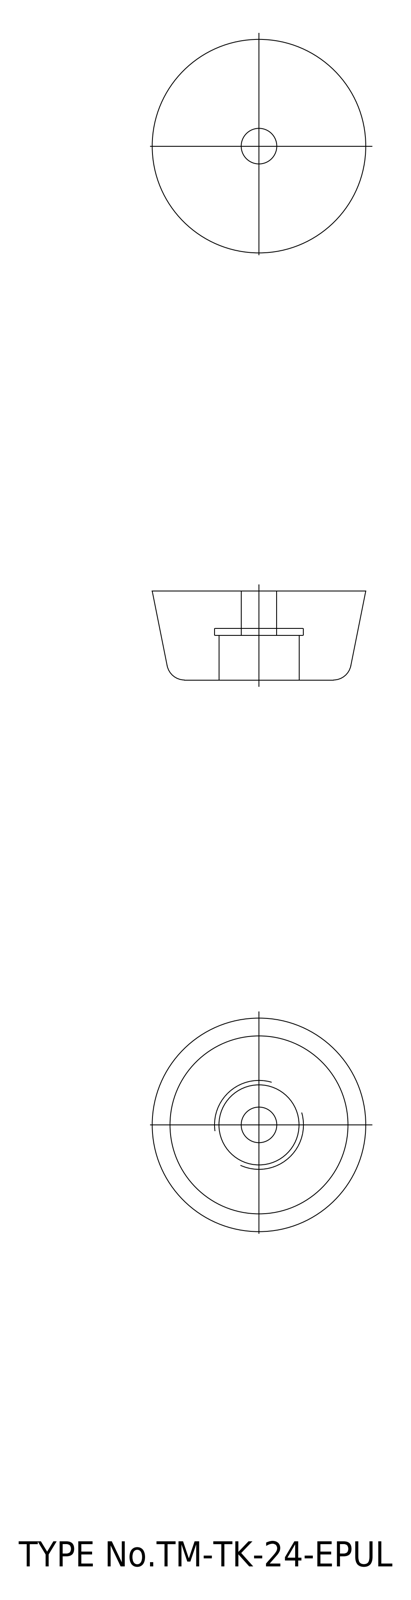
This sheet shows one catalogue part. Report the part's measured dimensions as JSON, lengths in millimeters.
{"part_name": "washer; rubber foot", "step_written_by": "spGate 15.6.1 (AUTOMOTIVE_DESIGN)", "units": "millimeters", "bodies": {"solids": 2, "faces": 20, "planar": 6, "cylindrical": 10, "other": 4}, "overall_size": [24, 24, 10], "volume_mm3": 3405, "surface_area_mm2": 1829, "round_holes": [[4, 1], [9, 1], [10, 1]], "face_to_face_distances": [5, 10, 5.8, 4.2, 0.8]}
